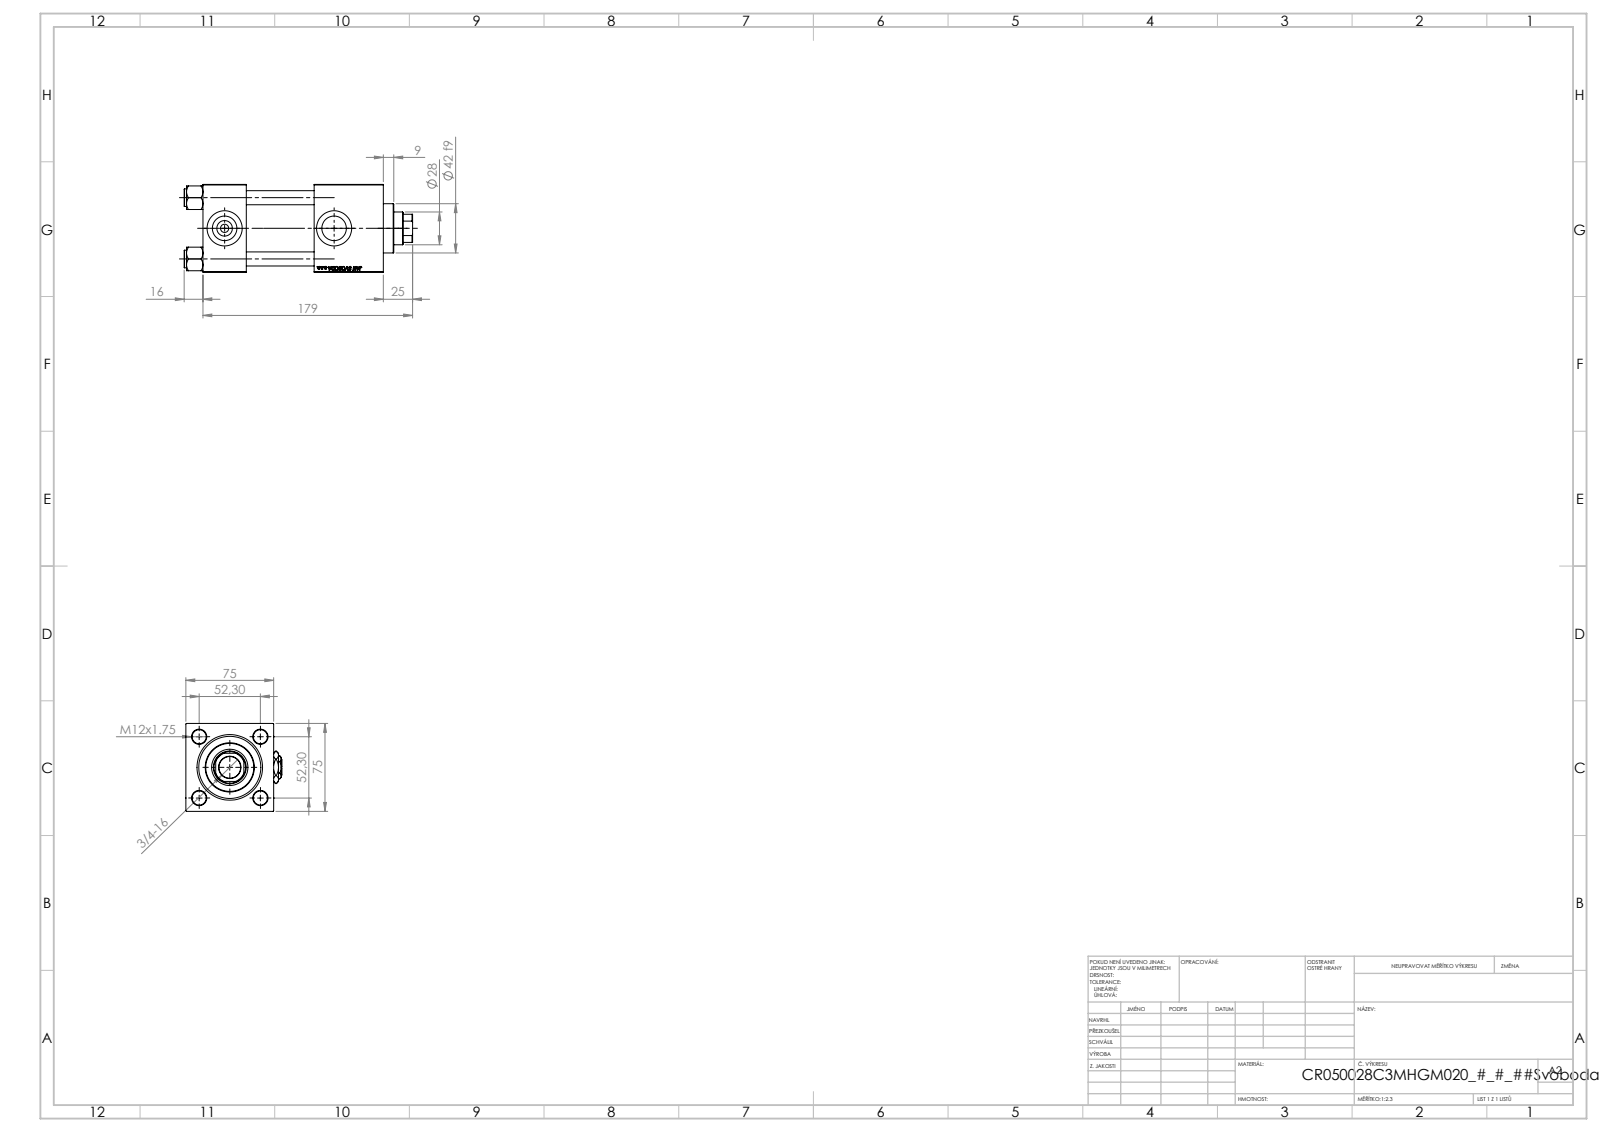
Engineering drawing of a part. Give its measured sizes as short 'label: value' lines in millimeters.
name: Zatka_pro_OIL_PORT; V215_VC_A; NUT_M5_C; V215CR_C_TYCINKA (+2 more)
written by: SolidWorks 2019 (CONFIG_CONTROL_DESIGN)
unit: mm
bodies: 13 solids, 1249 faces (573 planar, 98 cylindrical, 578 other)
size: 195 × 82.27 × 75
volume: 663 959 mm³; area: 155 409 mm²
holes: 4× ⌀12, 2× ⌀7, 2× ⌀20.96, 2× ⌀30, 1× ⌀18.5, 1× ⌀28, 1× ⌀31, 1× ⌀41, 1× ⌀50, 1× ⌀53
bosses: 4× ⌀15, 1× ⌀56, 1× ⌀42
rounds: 1× R13.5
face distances: 75, 37, 154, 117, 95, 58, 59, 125.3, 88.3, 30.3
hole spacings: 36.98, 52.3, 73.96, 93.5
